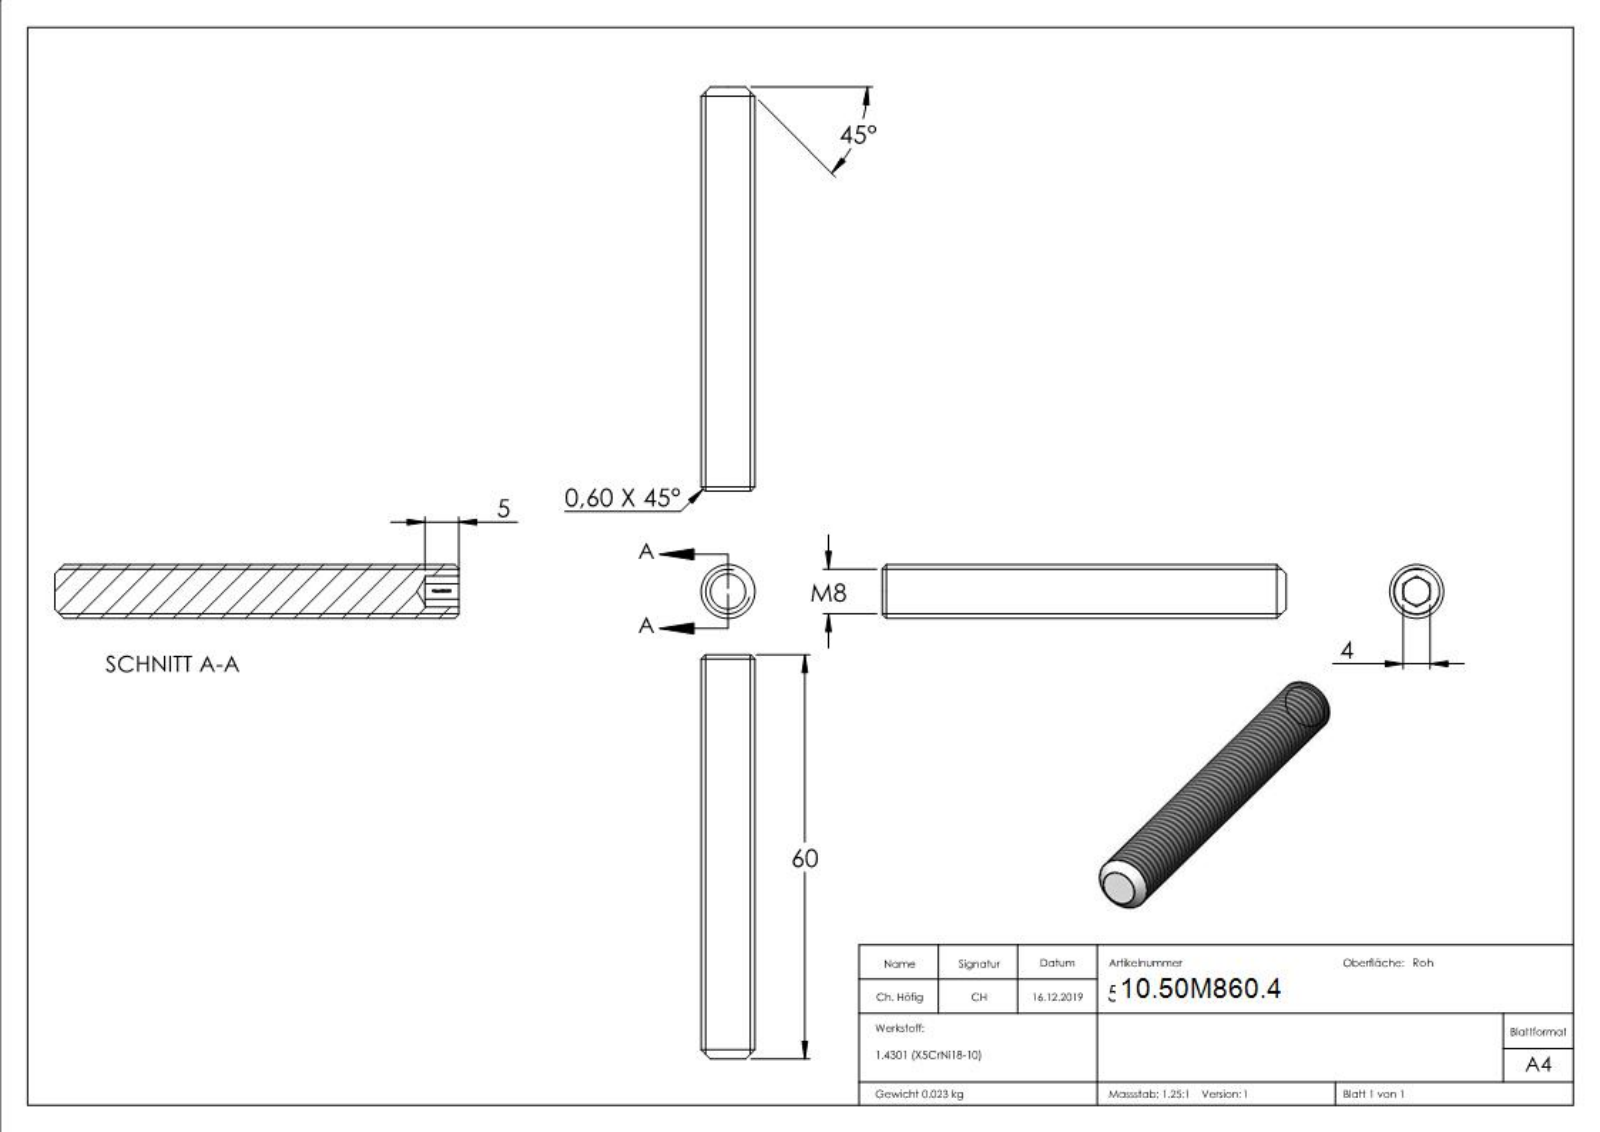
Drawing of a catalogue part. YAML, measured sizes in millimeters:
part_name: "58300-240-60"
step_written_by: "SolidWorks 2015 (CONFIG_CONTROL_DESIGN)"
units: millimeters
bodies: {solids: 1, faces: 297, planar: 135, cylindrical: 1, other: 161}
overall_size: [70, 8, 8]
volume: 2916
surface_area: 1649
round_bosses_or_shafts:
  - {diameter: 8, count: 1}
face_to_face_distances: [4, 60, 55, 5, 4.1, 0.48, 0.54, 1.67, 0.31, 1.6]
